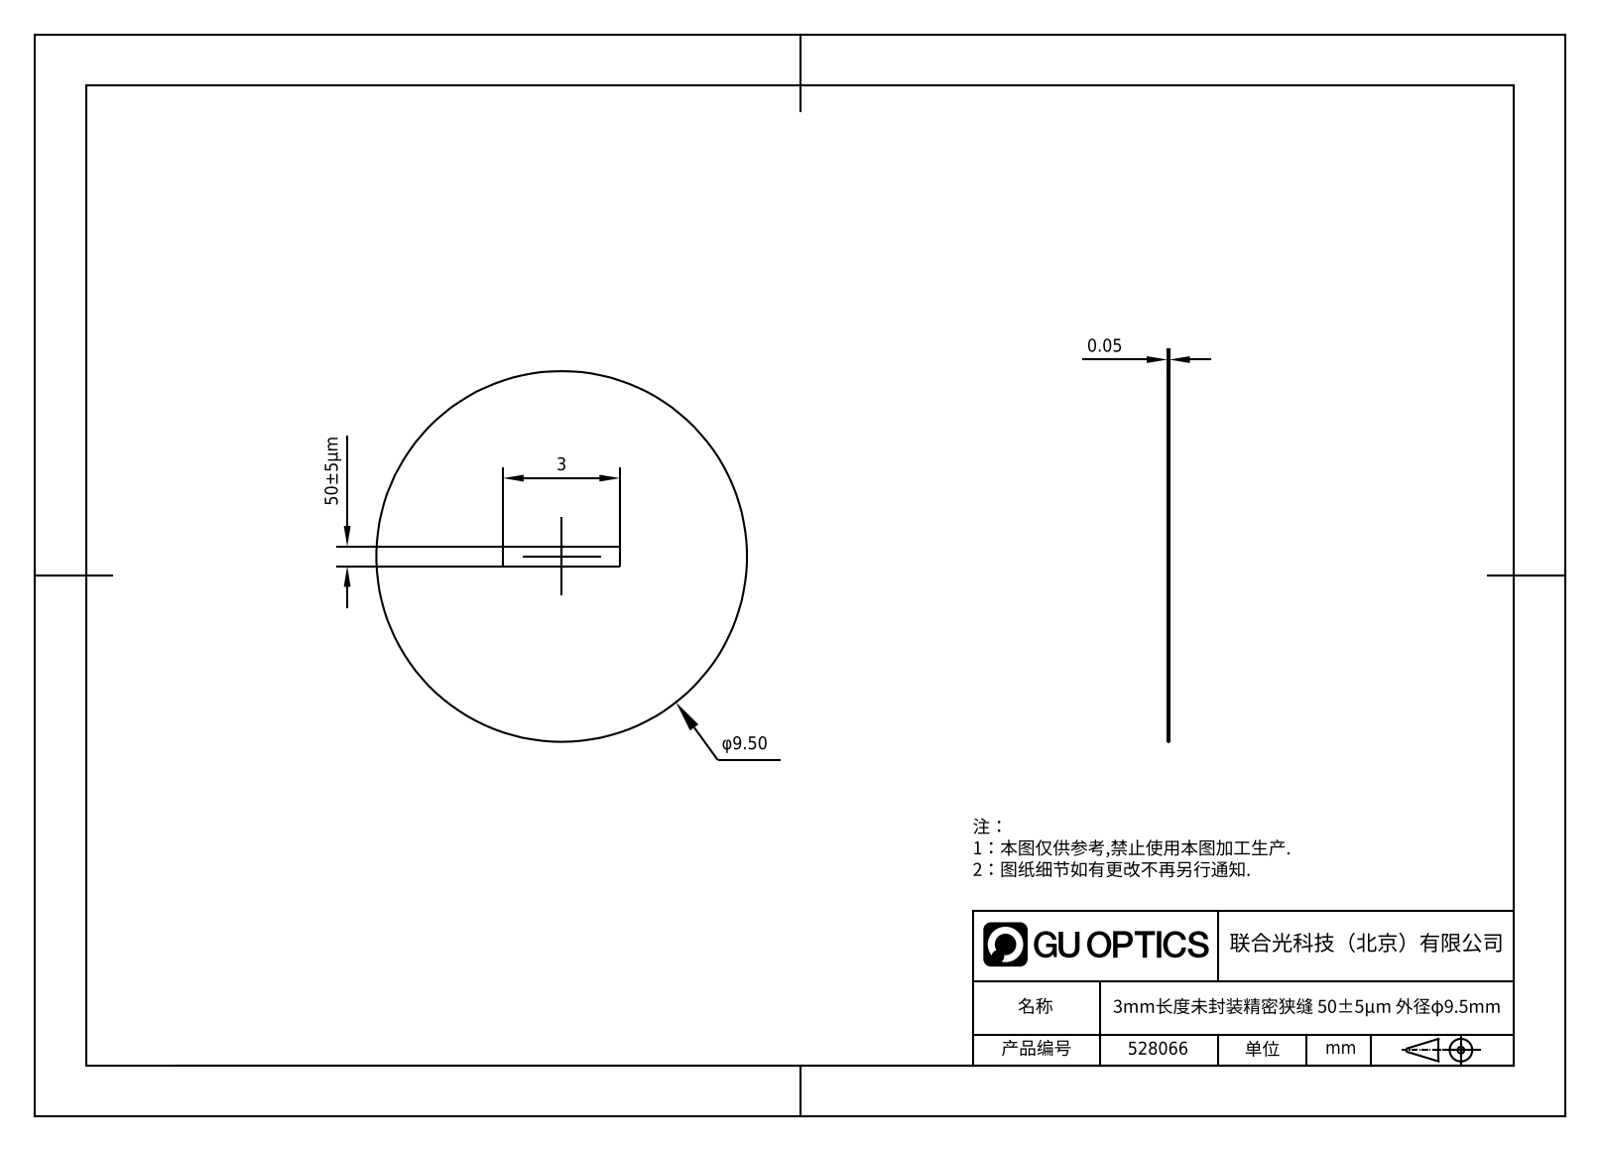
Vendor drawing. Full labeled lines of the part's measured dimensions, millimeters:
Part name (STEP PRODUCT): 1.5.4.7-ZXG-9.5-50
STEP written by: SolidWorks 2021 (CONFIG_CONTROL_DESIGN)
Units: millimetres
Bodies: 1 solid, 8 faces (6 planar, 2 cylindrical, 0 other)
Overall size (bounding box): 9.5 × 9.5 × 0.05
Volume: 4 mm³ · Surface area: 143 mm²
Round bosses / shafts (diameter × count): ⌀9.5 ×1
Main face-to-face distances: 3
